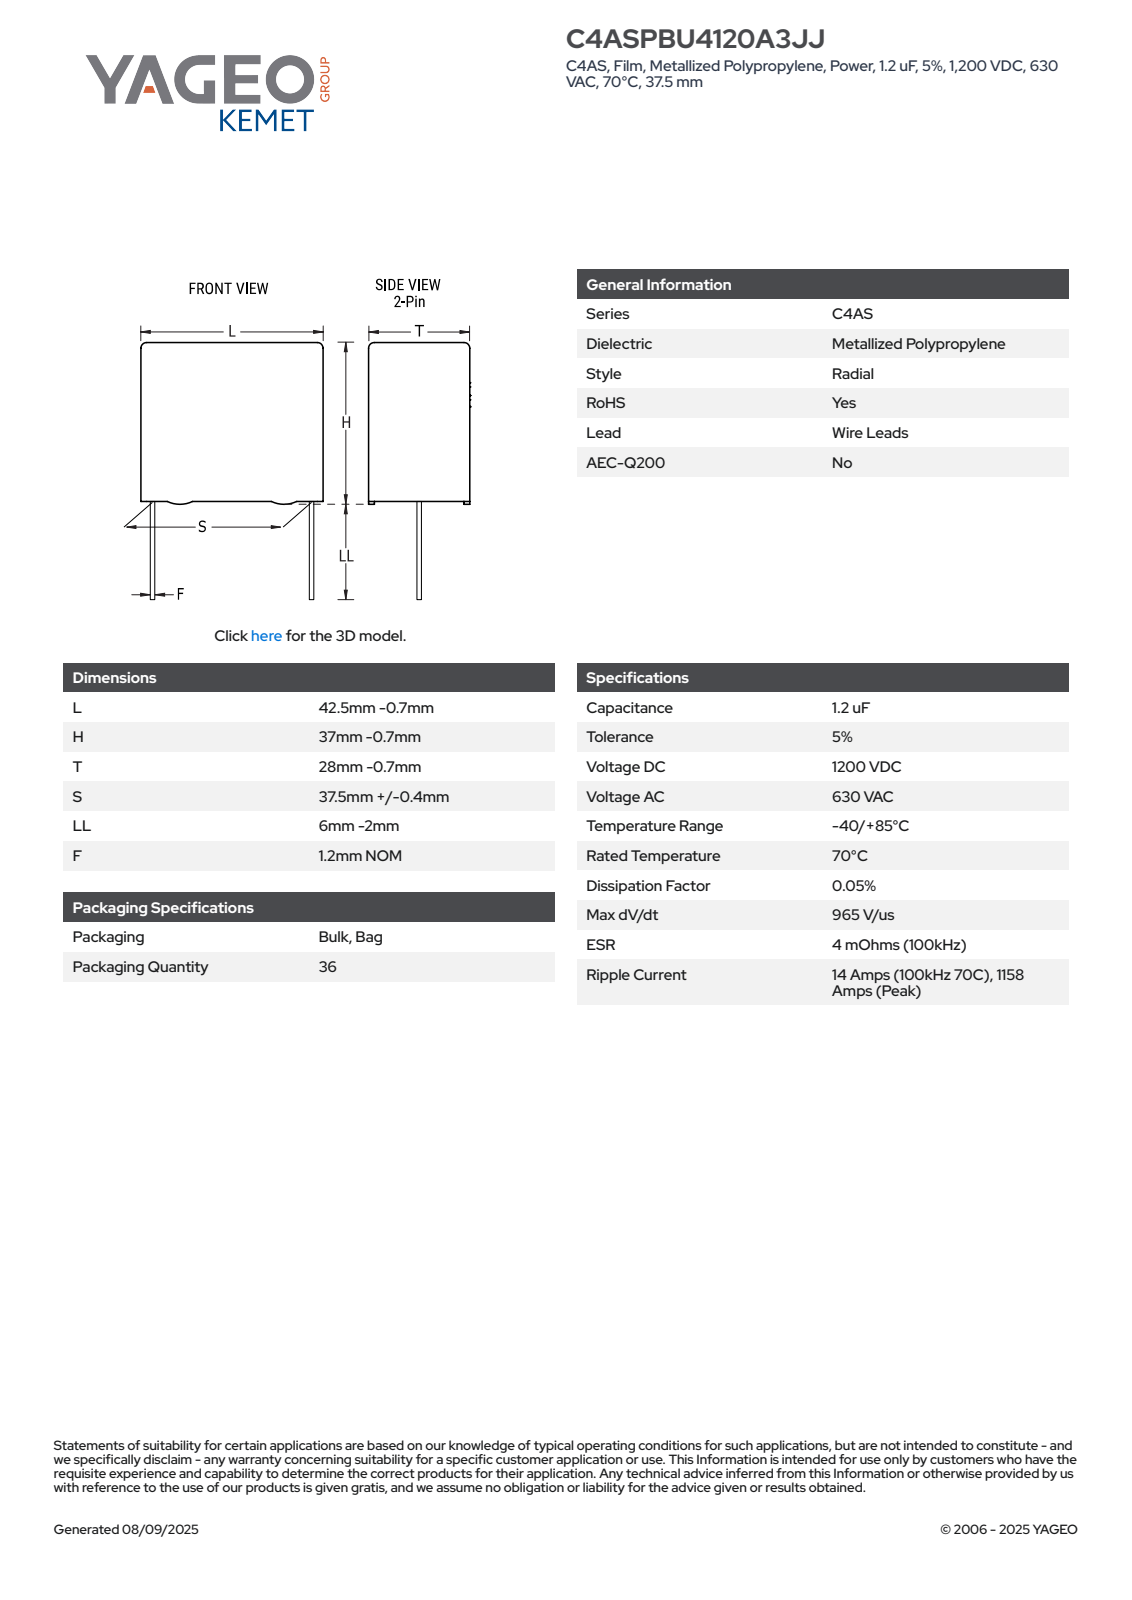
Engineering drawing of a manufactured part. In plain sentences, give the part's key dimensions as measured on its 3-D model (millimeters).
The part is named "CFP_RB_42.5X37X28_L41.8H36.3T27.3S37.5LL4F1.2". Its 3-D file was written by "SolidWorks 2014 (AUTOMOTIVE_DESIGN)". It is 4 solids with 89 faces: 81 planar, 8 cylindrical and 0 other. Overall it measures 41.8 by 40.3 by 27.3 millimeters. Its volume is 40 625 cubic millimeters and its surface area 7 327 square millimeters. Round bosses or shafts: 2 of diameter 1.2. Partial cylindrical surfaces (rounded edges, fillets, slot ends): 4 of radius 0.5. The main face-to-face distances are 27.3, 35.57, 41.8, 0.73, 36.3, 27.31, 1.56, 25.74, 1.57, 24.18.
